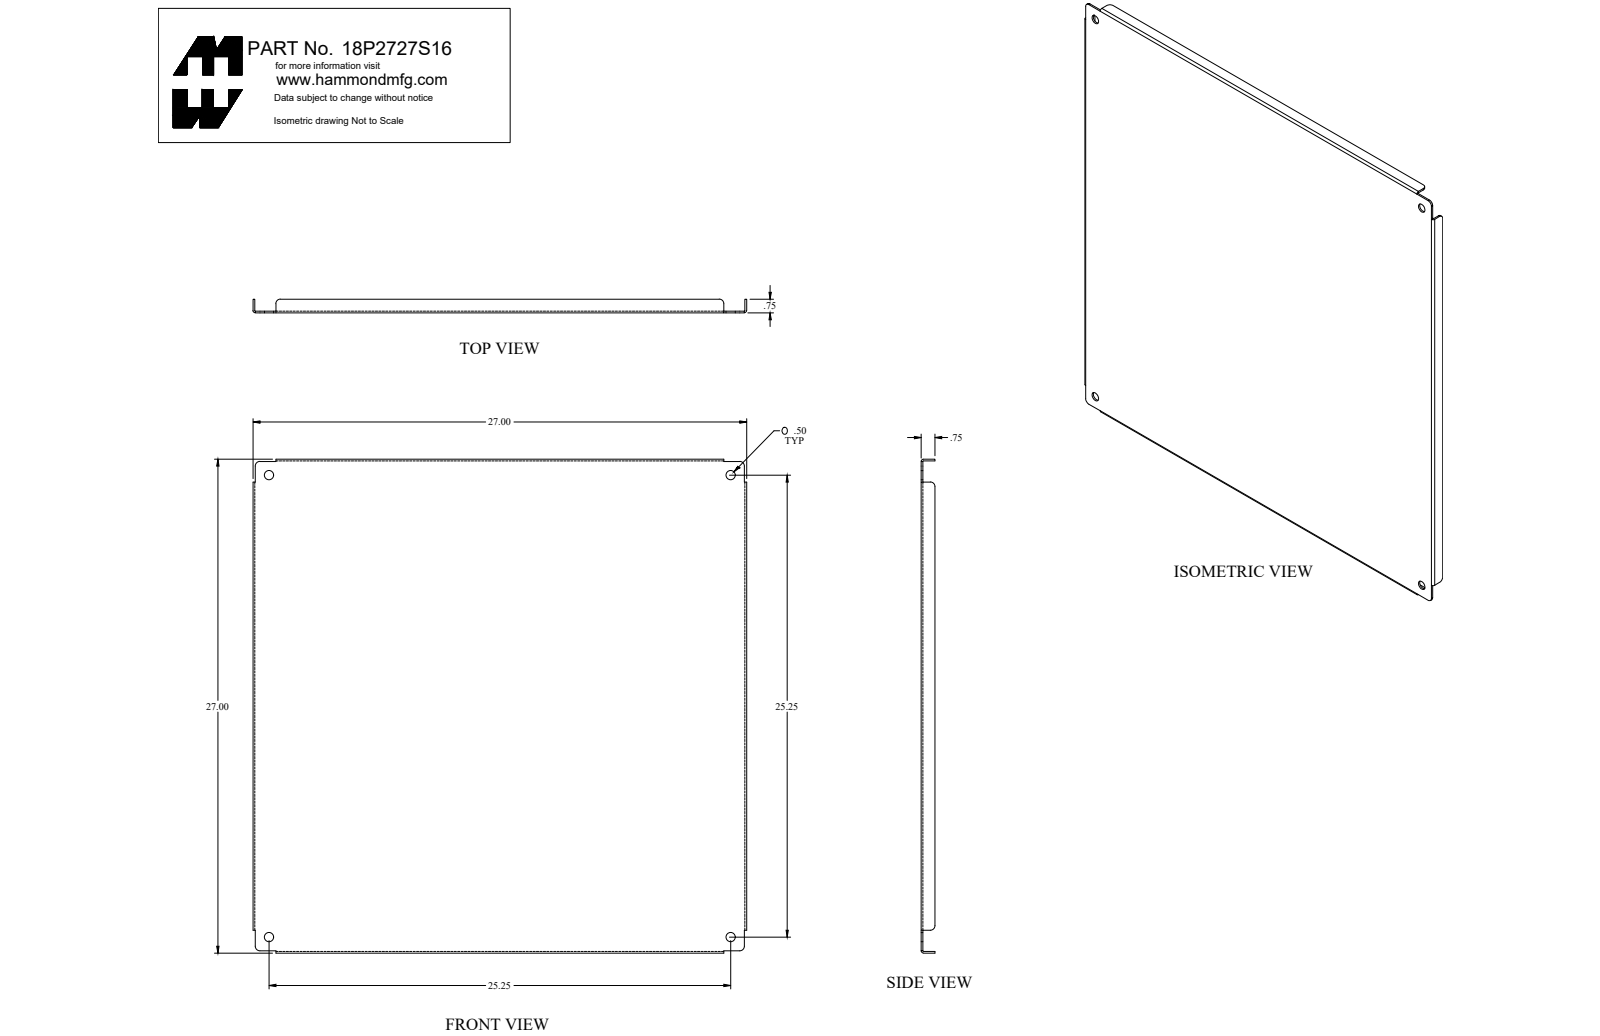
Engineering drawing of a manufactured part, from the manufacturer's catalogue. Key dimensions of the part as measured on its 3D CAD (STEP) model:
Part name (STEP PRODUCT): 18P2727S16_Default
STEP written by: SolidWorks 2018 (CONFIG_CONTROL_DESIGN)
Units: inches
Bodies: 1 solid, 58 faces (30 planar, 28 cylindrical, 0 other)
Overall size (bounding box): 27 × 27 × 0.75
Volume: 74.84 in³ · Surface area: 1 587 in²
Round holes (diameter × count): ⌀0.5 ×4
Partial cylindrical surfaces — rounded edges, fillets, slot ends (radius × count): R0.25 ×8, R0.03 ×4, R0.125 ×4
Main face-to-face distances: 0.095, 26.905, 27, 26.81, 0.75, 0.655, 0.125, 26.875, 0.03, 26.78
Hole centre spacings: 25.25, 35.709
